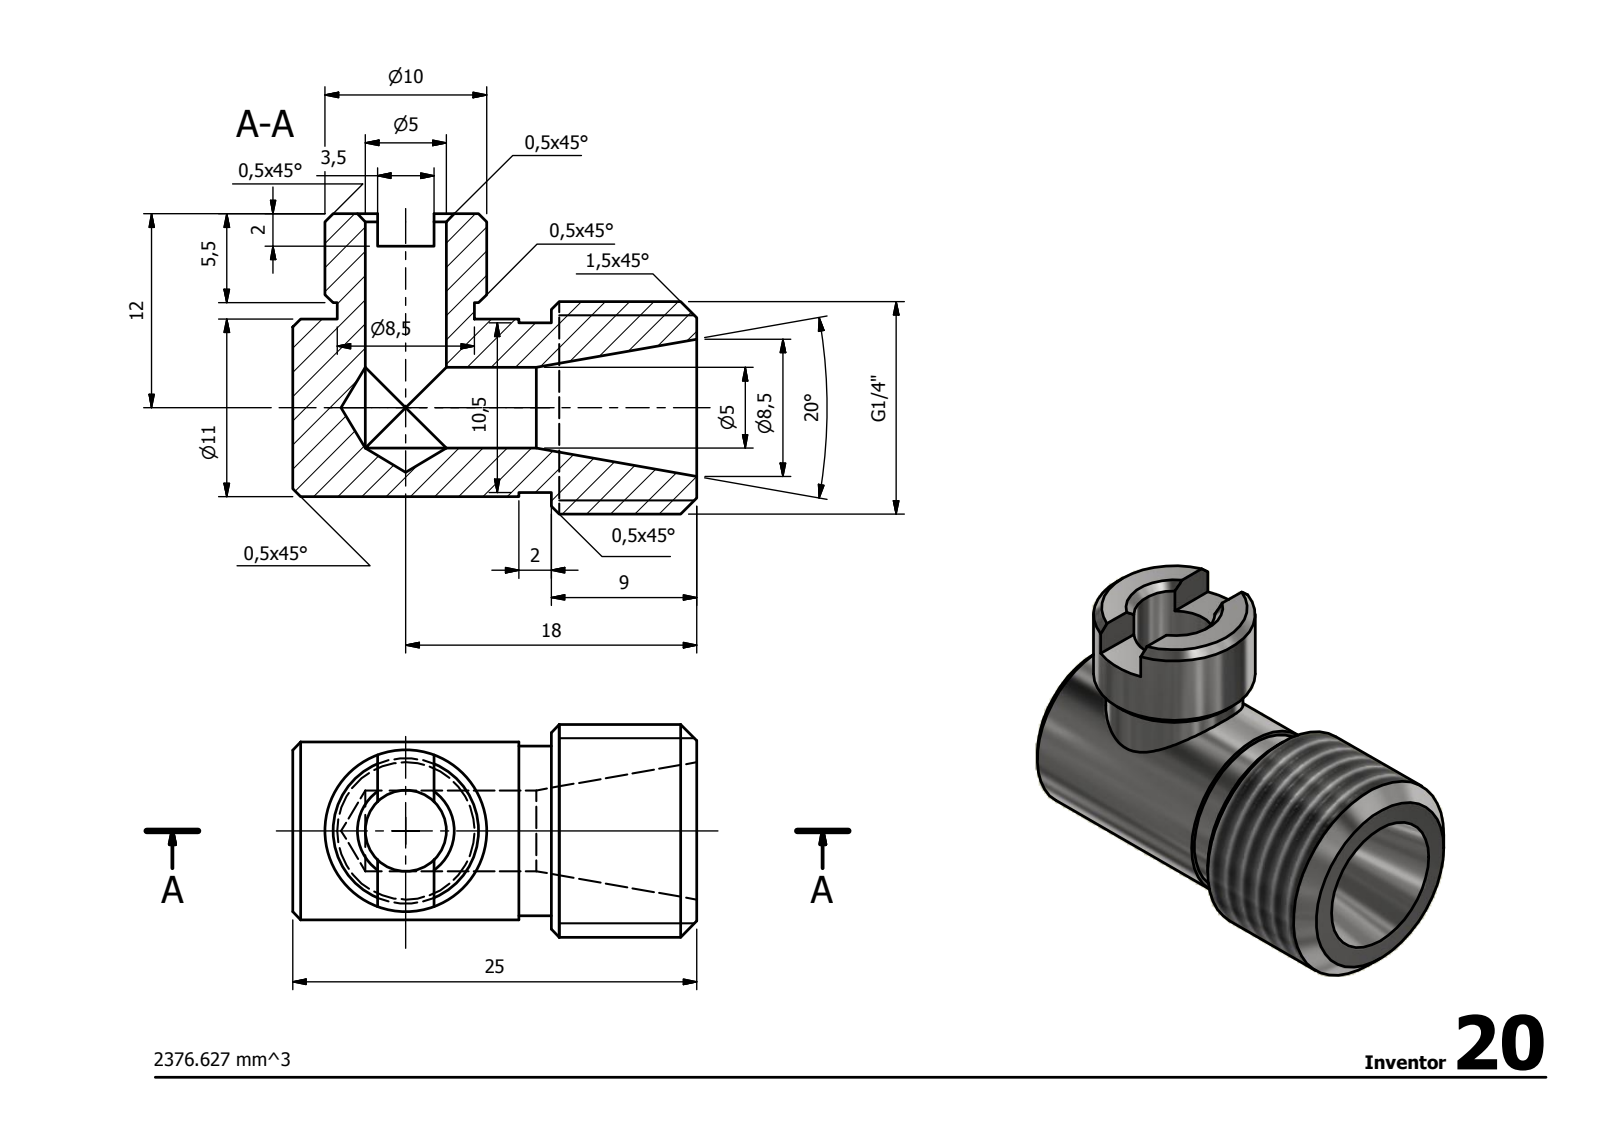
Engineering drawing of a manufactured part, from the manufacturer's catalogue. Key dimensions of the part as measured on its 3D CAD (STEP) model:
STEP written by: Autodesk Inventor 2014 (AUTOMOTIVE_DESIGN)
Units: millimetres
Bodies: 1 solid, 35 faces (13 planar, 11 cylindrical, 11 other)
Overall size (bounding box): 25 × 18.58 × 13.16
Volume: 2 376 mm³ · Surface area: 1 875 mm²
Round holes (diameter × count): ⌀5 ×2
Round bosses / shafts (diameter × count): ⌀13.16 ×1, ⌀11 ×1, ⌀10.5 ×1, ⌀10 ×1, ⌀8.5 ×1
Main face-to-face distances: 25, 16, 9, 2, 5.25, 8.75, 3.5, 10.75, 19.75, 7.25
